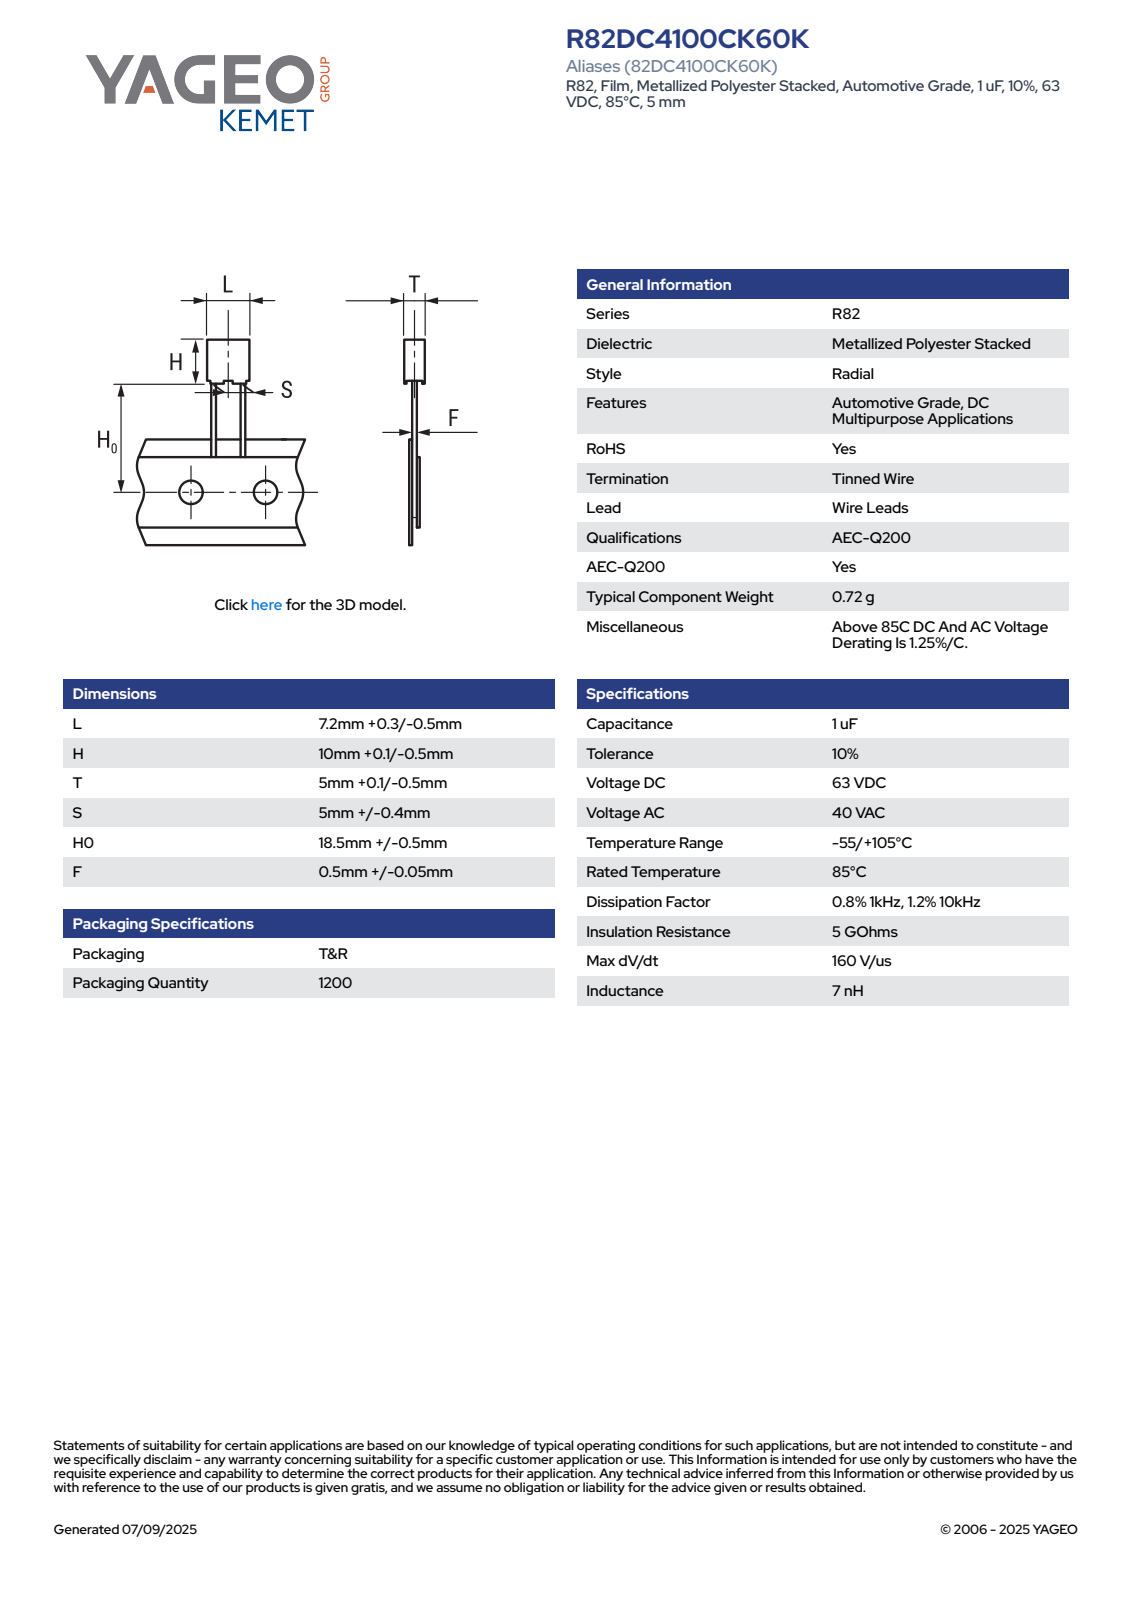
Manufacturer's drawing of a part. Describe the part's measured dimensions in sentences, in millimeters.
The part is named "CFR_RB3_7.2X10X5_L7.5H10.1T5.1S5H019F0.55". Its 3-D file was written by "SolidWorks 2014 (AUTOMOTIVE_DESIGN)". It is 4 solids with 85 faces: 77 planar, 8 cylindrical and 0 other. Overall it measures 29.1 by 7.5 by 5.11 millimeters. Its volume is 370 cubic millimeters and its surface area 413 square millimeters. Round bosses or shafts: 2 of diameter 0.55. Partial cylindrical surfaces (rounded edges, fillets, slot ends): 4 of radius 0.5. The main face-to-face distances are 5.1, 7.5, 9.35, 4.85, 7.25, 0.75, 10.1, 4.6, 7, 0.35.
